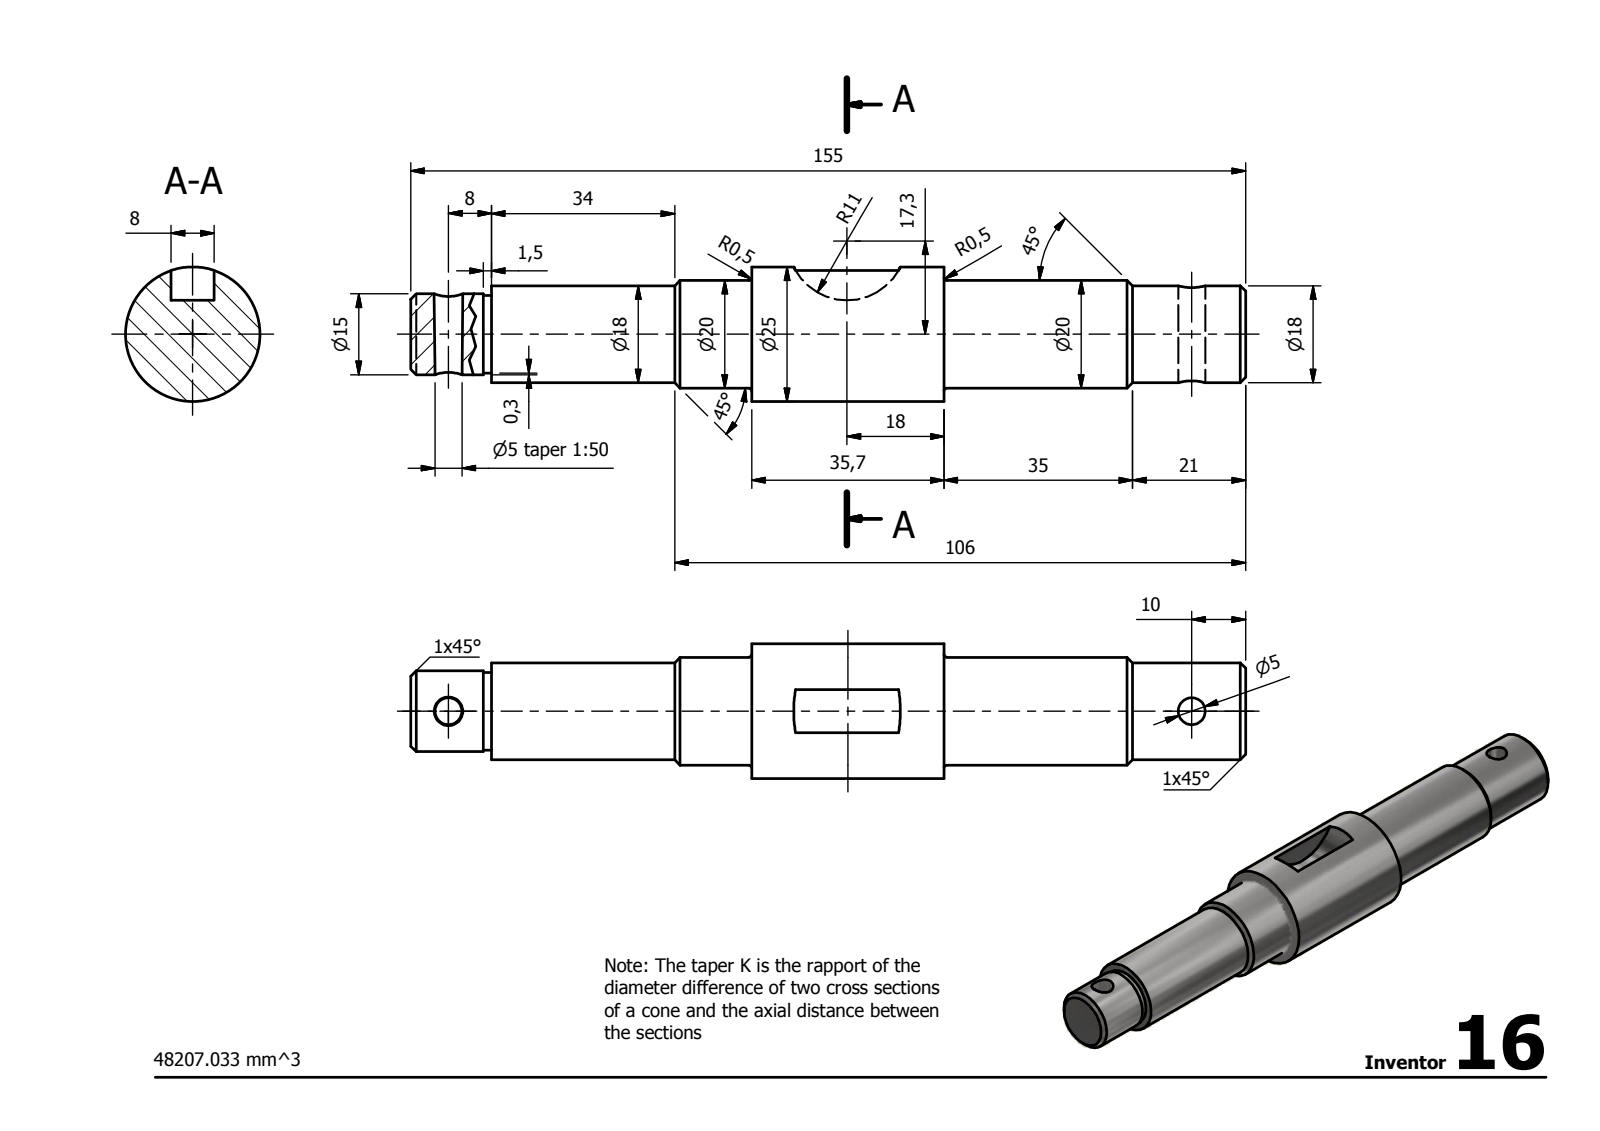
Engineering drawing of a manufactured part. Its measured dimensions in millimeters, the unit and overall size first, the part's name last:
Units: millimetres
Overall size (bounding box): 155 × 25 × 25
Round holes (diameter × count): ⌀5 ×1
Round bosses / shafts (diameter × count): ⌀25 ×1, ⌀20 ×1, ⌀18 ×1, ⌀15 ×1, ⌀14.4 ×1
Partial cylindrical surfaces — rounded edges, fillets, slot ends (radius × count): R11 ×1
Main face-to-face distances: 56, 35.7, 91.7, 63.3, 99, 155, 15, 48.3, 84, 140
Volume: 48 207 mm³ · Surface area: 11 173 mm²
Bodies: 1 solid, 24 faces (8 planar, 9 cylindrical, 7 other)
STEP written by: Autodesk Inventor 2014 (AUTOMOTIVE_DESIGN)
